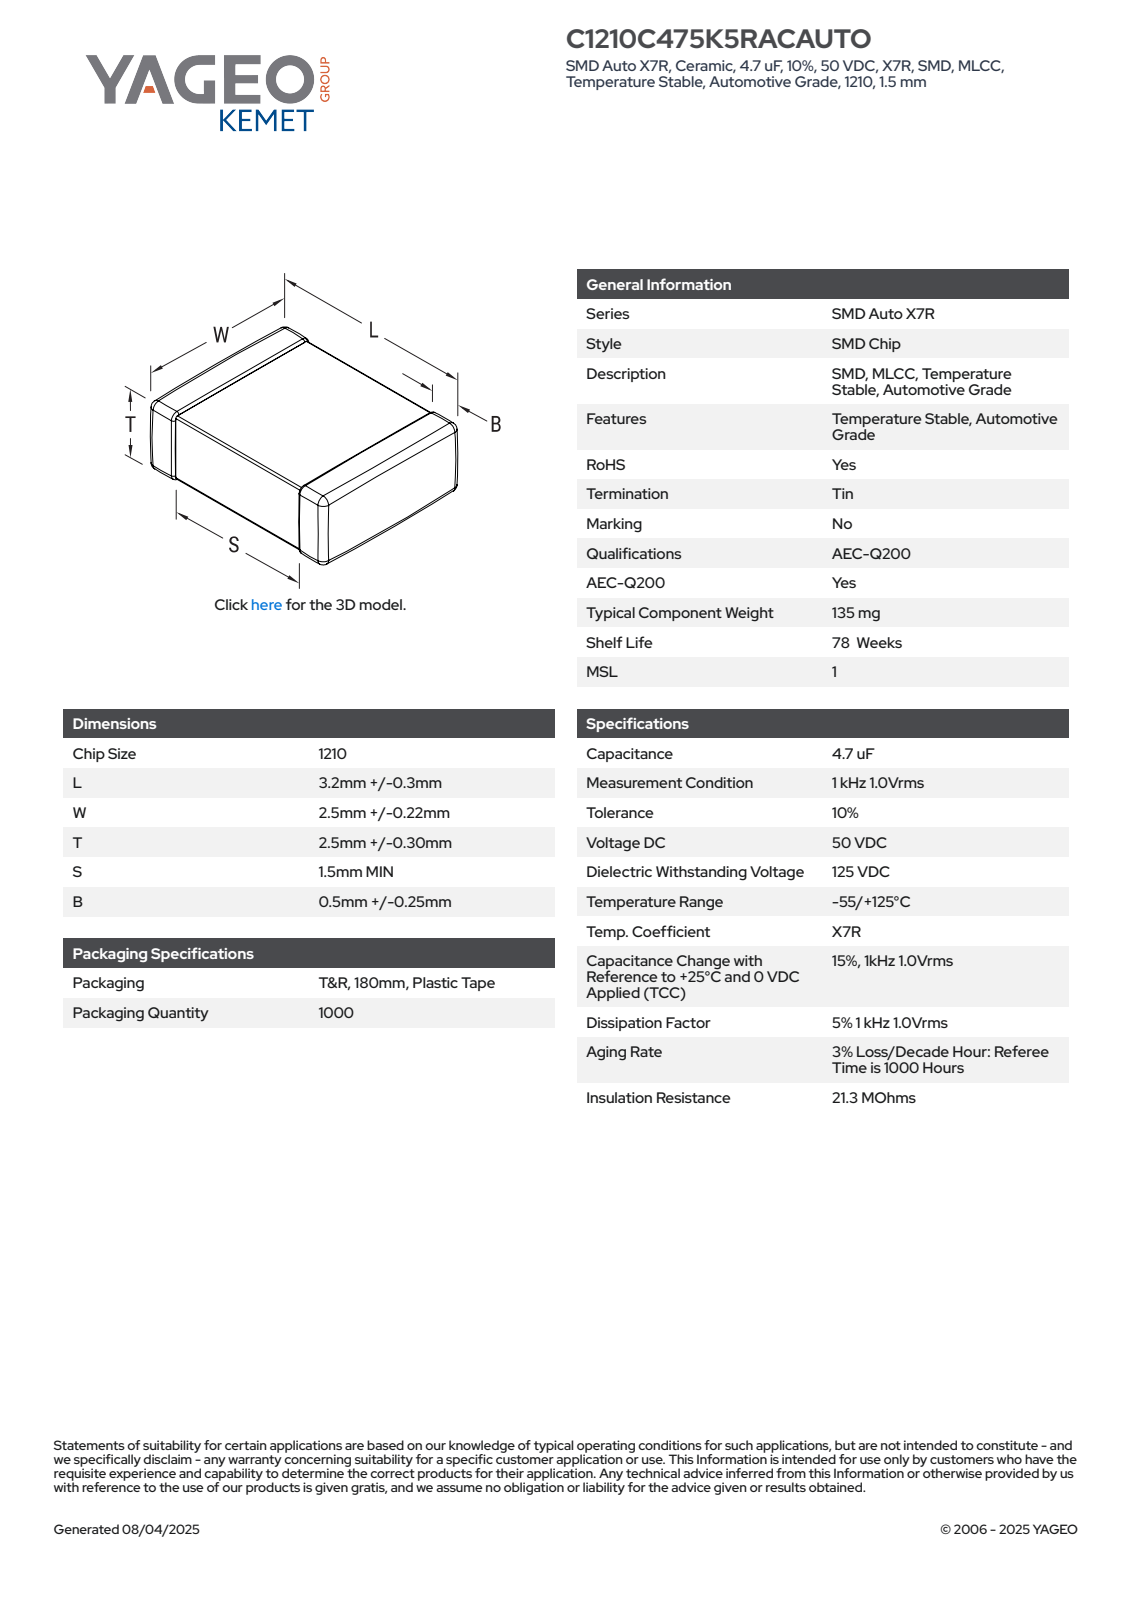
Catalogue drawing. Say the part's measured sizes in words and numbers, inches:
The part is named "CCS_CCSTDNOS_1210_L3.5W2.72T2.8B0.75". Its 3-D file was written by "SolidWorks 2014 (AUTOMOTIVE_DESIGN)". It is 4 solids with 125 faces: 71 planar, 38 cylindrical and 16 other. Overall it measures 0.138 by 0.11 by 0.107 inches. Its volume is 0.002 cubic inches and its surface area 0.082 square inches. The main face-to-face distances are 0.138, 0.105, 0.108, 0.102, 0.106, 0.107, 0.11, 0.108, 0.106, 0.052.
